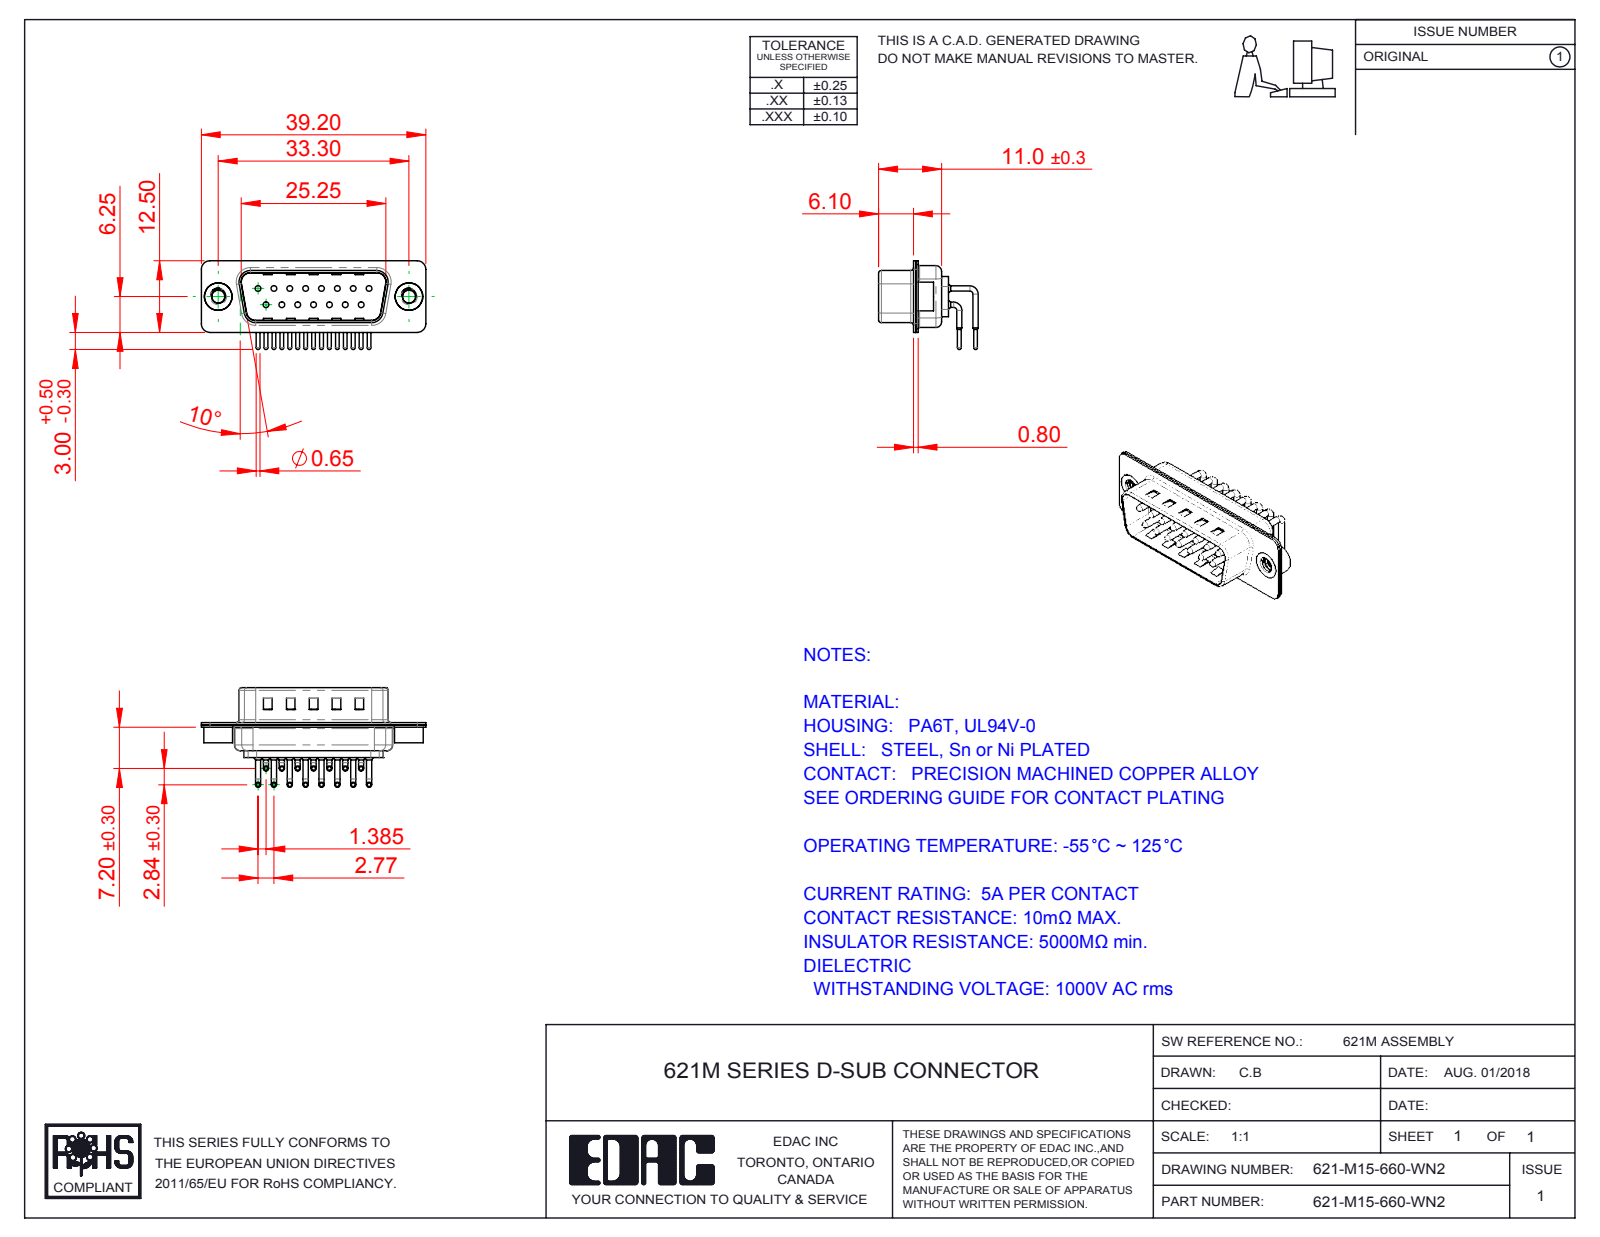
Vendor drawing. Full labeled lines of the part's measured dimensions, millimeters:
Part name (STEP PRODUCT): 621M Contact Row 1; 621M Shell Front_15 Contacts; 621M Housing_15 Contacts; 621M Shell Rear_15 Contacts (+3 more)
STEP written by: SolidWorks 2016 (CONFIG_CONTROL_DESIGN)
Units: millimetres
Bodies: 20 solids, 1990 faces (1099 planar, 673 cylindrical, 218 other)
Overall size (bounding box): 39.2 × 17.39 × 15.49
Volume: 1 938 mm³ · Surface area: 5 262 mm²
Round holes (diameter × count): ⌀1 ×15, ⌀1.7 ×15, ⌀2 ×15, ⌀2.26 ×2, ⌀4 ×2, ⌀4.8 ×2
Round bosses / shafts (diameter × count): ⌀0.9 ×30, ⌀1.5 ×15, ⌀0.65 ×15, ⌀5 ×2, ⌀4.9 ×2
Partial cylindrical surfaces — rounded edges, fillets, slot ends (radius × count): R1.5 ×16, R1.01 ×15, R2 ×12, R0.5 ×8, R1.6 ×8, R0.25 ×4, R0.6 ×4, R0.65 ×4
Main face-to-face distances: 0.4, 0.85, 9.55, 8.7, 1.25, 10.4, 0.8, 1.5, 0.35, 1.9
Hole centre spacings: 3.16, 2.77, 5.54, 8.31, 11.08, 5.03, 5.04, 7.48
